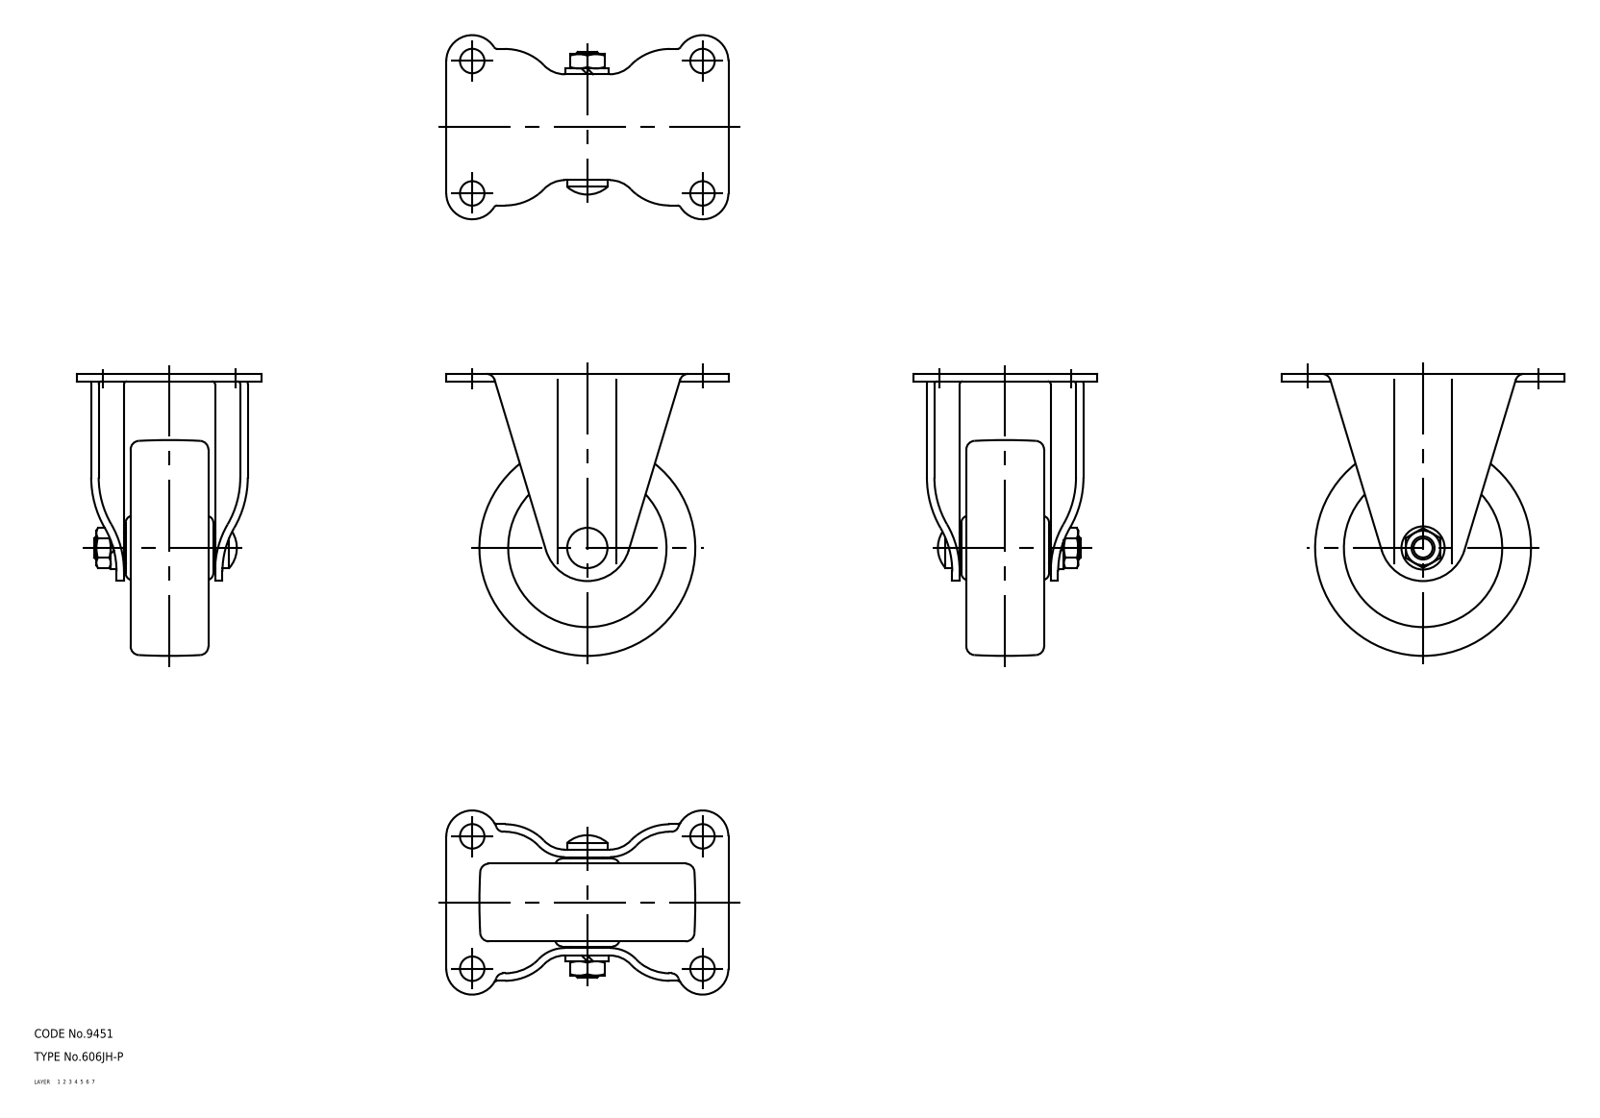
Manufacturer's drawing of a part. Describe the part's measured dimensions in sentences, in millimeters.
The part is named "wheel; axle; No_606JH_P_16971_36". Its 3-D file was written by "CADfix (AUTOMOTIVE_DESIGN)". It is 3 solids with 196 faces: 0 planar, 0 cylindrical and 196 other. Overall it measures 98 by 98 by 64 millimeters. Its volume is 125 734 cubic millimeters and its surface area 42 910 square millimeters.
